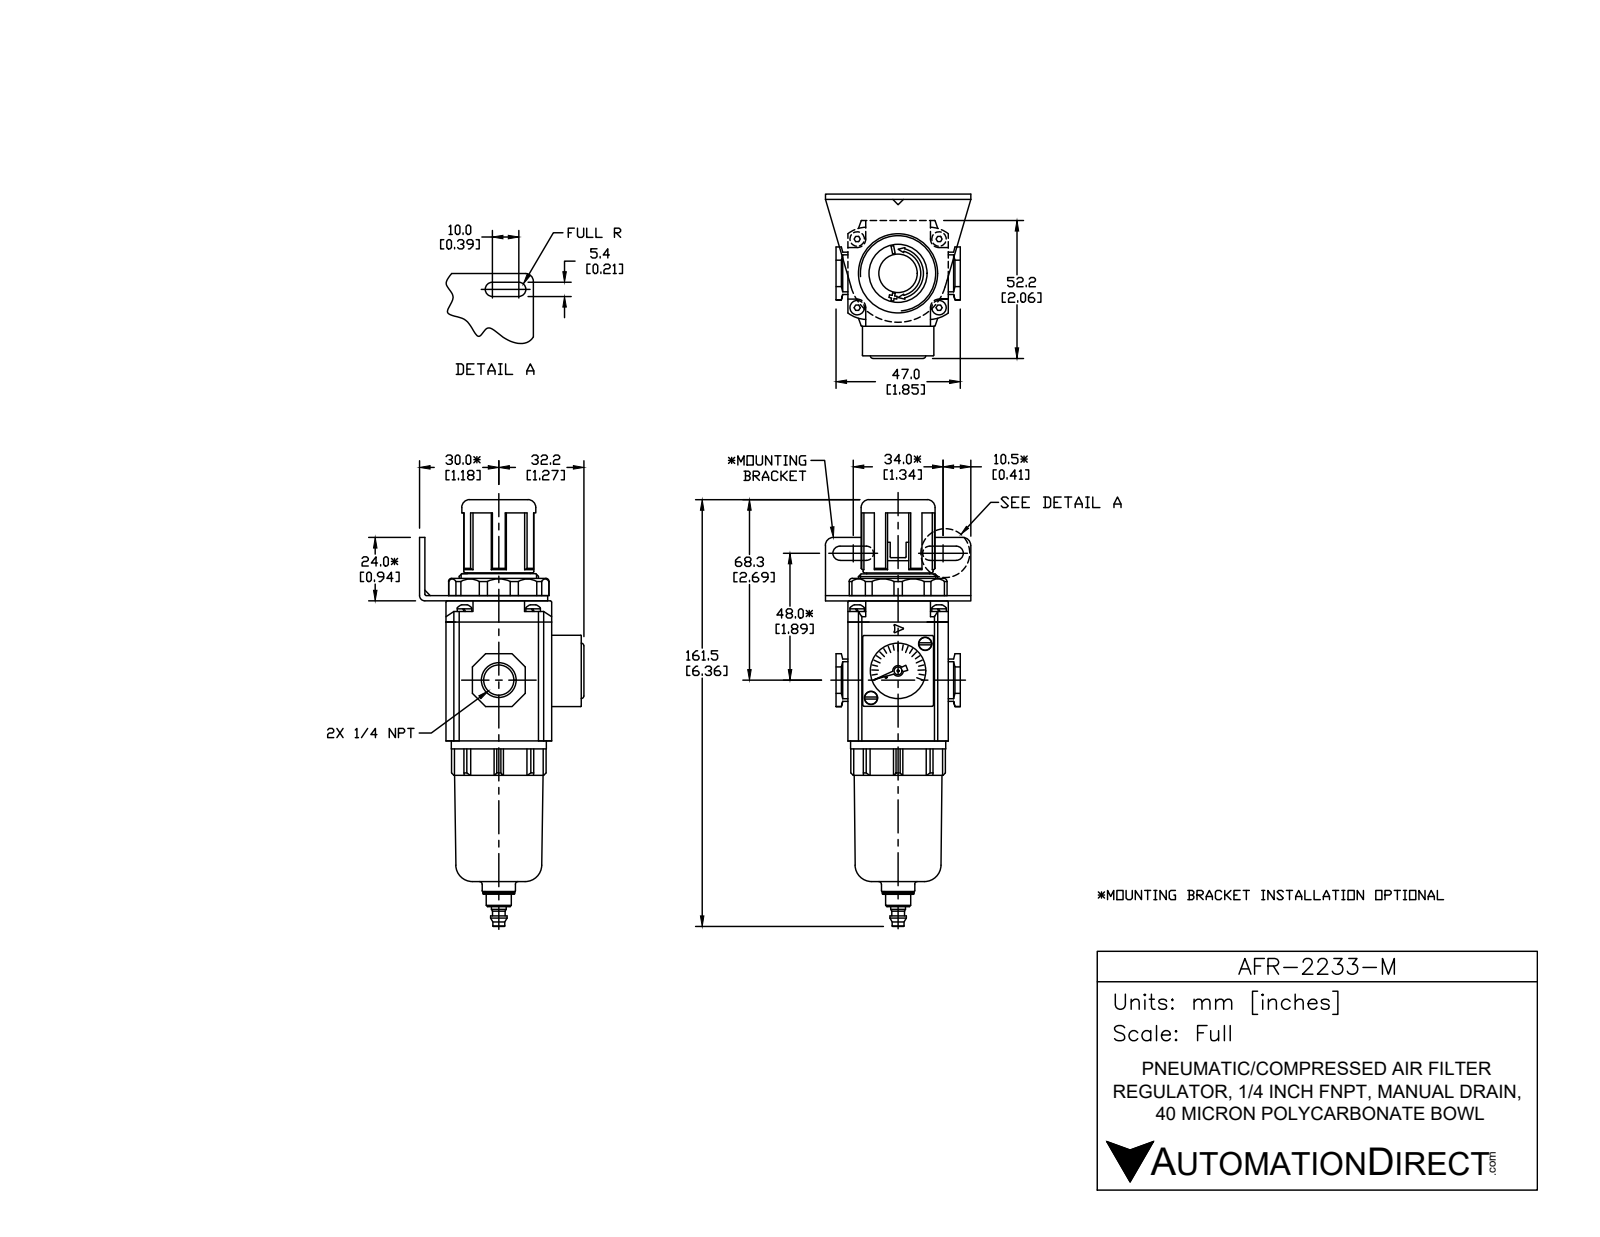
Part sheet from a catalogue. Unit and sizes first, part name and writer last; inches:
Units: inches
Overall size (bounding box): 6.346 × 2.441 × 2.165
Round holes (diameter × count): ⌀0.118 ×7, ⌀0.079 ×1, ⌀0.438 ×1, ⌀0.827 ×1, ⌀0.866 ×1, ⌀1.004 ×1, ⌀1.181 ×1
Round bosses / shafts (diameter × count): ⌀0.217 ×4, ⌀0.106 ×2, ⌀1.102 ×1, ⌀1.024 ×1, ⌀0.937 ×1, ⌀0.551 ×1, ⌀0.496 ×1, ⌀0.472 ×1
Partial cylindrical surfaces — rounded edges, fillets, slot ends (radius × count): R0.039 ×12, R0.047 ×10, R0.128 ×6, R0.012 ×4, R0.108 ×4, R0.472 ×4, R0.008 ×3, R0.079 ×1
Main face-to-face distances: 0.079, 2.165, 1.575, 2.087, 1.496, 1.535, 0.394, 0.039, 1.969, 0.433
Hole centre spacings: 0.796, 0.571, 1.024, 1.22, 1.593, 1.141
Volume: 8.079 in³ · Surface area: 63.1 in²
Bodies: 15 solids, 548 faces (329 planar, 159 cylindrical, 60 other)
Part name (STEP PRODUCT): AFR-2233-M
STEP written by: SolidWorks 2015 (CONFIG_CONTROL_DESIGN)
